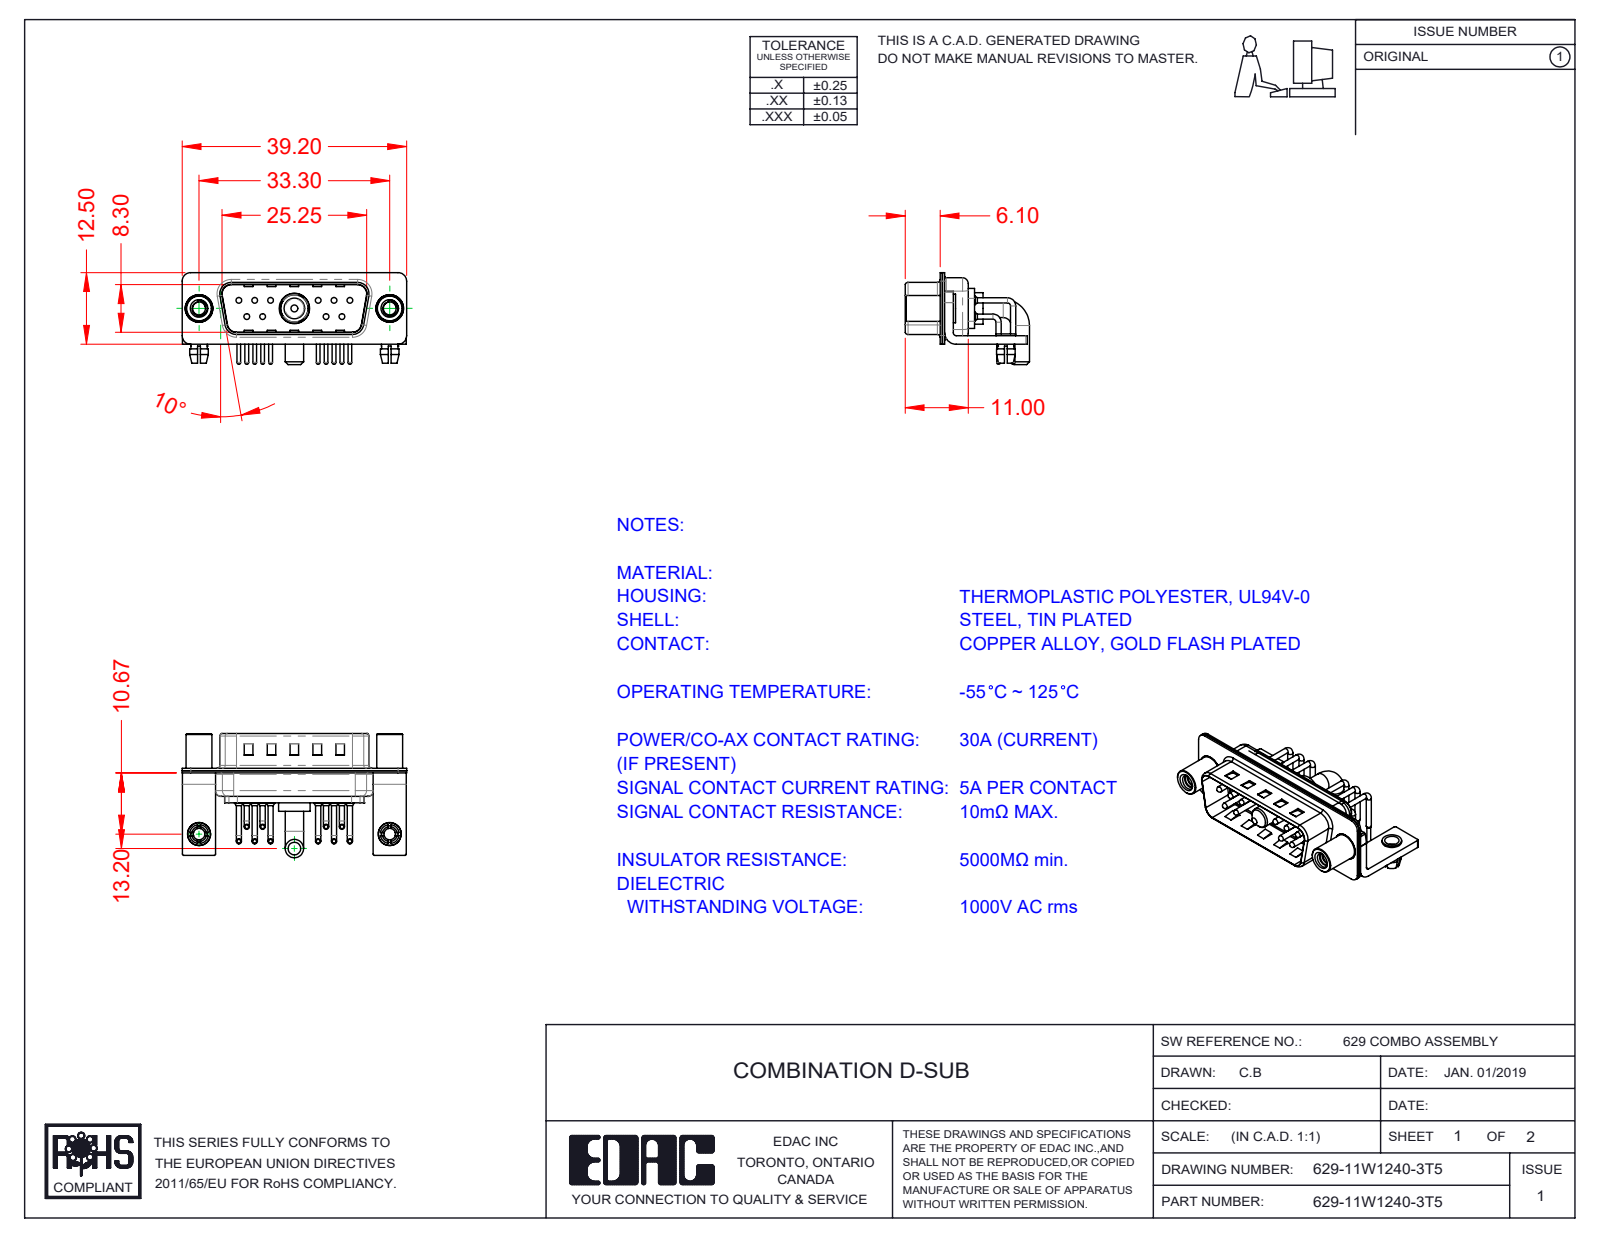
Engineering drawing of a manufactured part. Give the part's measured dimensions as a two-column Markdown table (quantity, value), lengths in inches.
| quantity | value |
| --- | --- |
| part name | 629Combo Contact Row 1; 629Combo Stabilizer Bracket; Power Pin_30A RA; 629Combo Shell Rear_15 Contacts (+6 more) |
| STEP written by | SolidWorks 2020 (CONFIG_CONTROL_DESIGN) |
| units | inches |
| bodies | 21 solids, 1676 faces (868 planar, 610 cylindrical, 198 other) |
| overall size | 1.543 × 0.854 × 0.632 |
| volume | 0.154 in³ |
| surface area | 9.884 in² |
| round holes (diameter × count) | 0.079 × 12, 0.03 × 10, 0.063 × 10, 0.089 × 2, 0.098 × 2, 0.126 × 2, 0.157 × 2, 0.189 × 2, 0.191 × 1, 0.209 × 1 |
| round bosses / shafts (diameter × count) | 0.035 × 20, 0.059 × 10, 0.039 × 10, 0.026 × 10, 0.197 × 2, 0.193 × 2, 0.177 × 2, 0.157 × 2 |
| partial cylindrical surfaces (radius × count) | 0.01 × 16, 0.059 × 16, 0.079 × 13, 0.04 × 10, 0.02 × 9, 0.063 × 8, 0.039 × 7, 0.024 × 4 |
| main face-to-face distances | 0.016, 0.031, 0.059, 0.374, 0.343, 0.358, 0.39, 0.024, 0.075, 0.205 |
| hole center spacings | 0.124, 0.109, 0.545, 0.436, 0.654, 0.198, 0.198, 0.218 |
